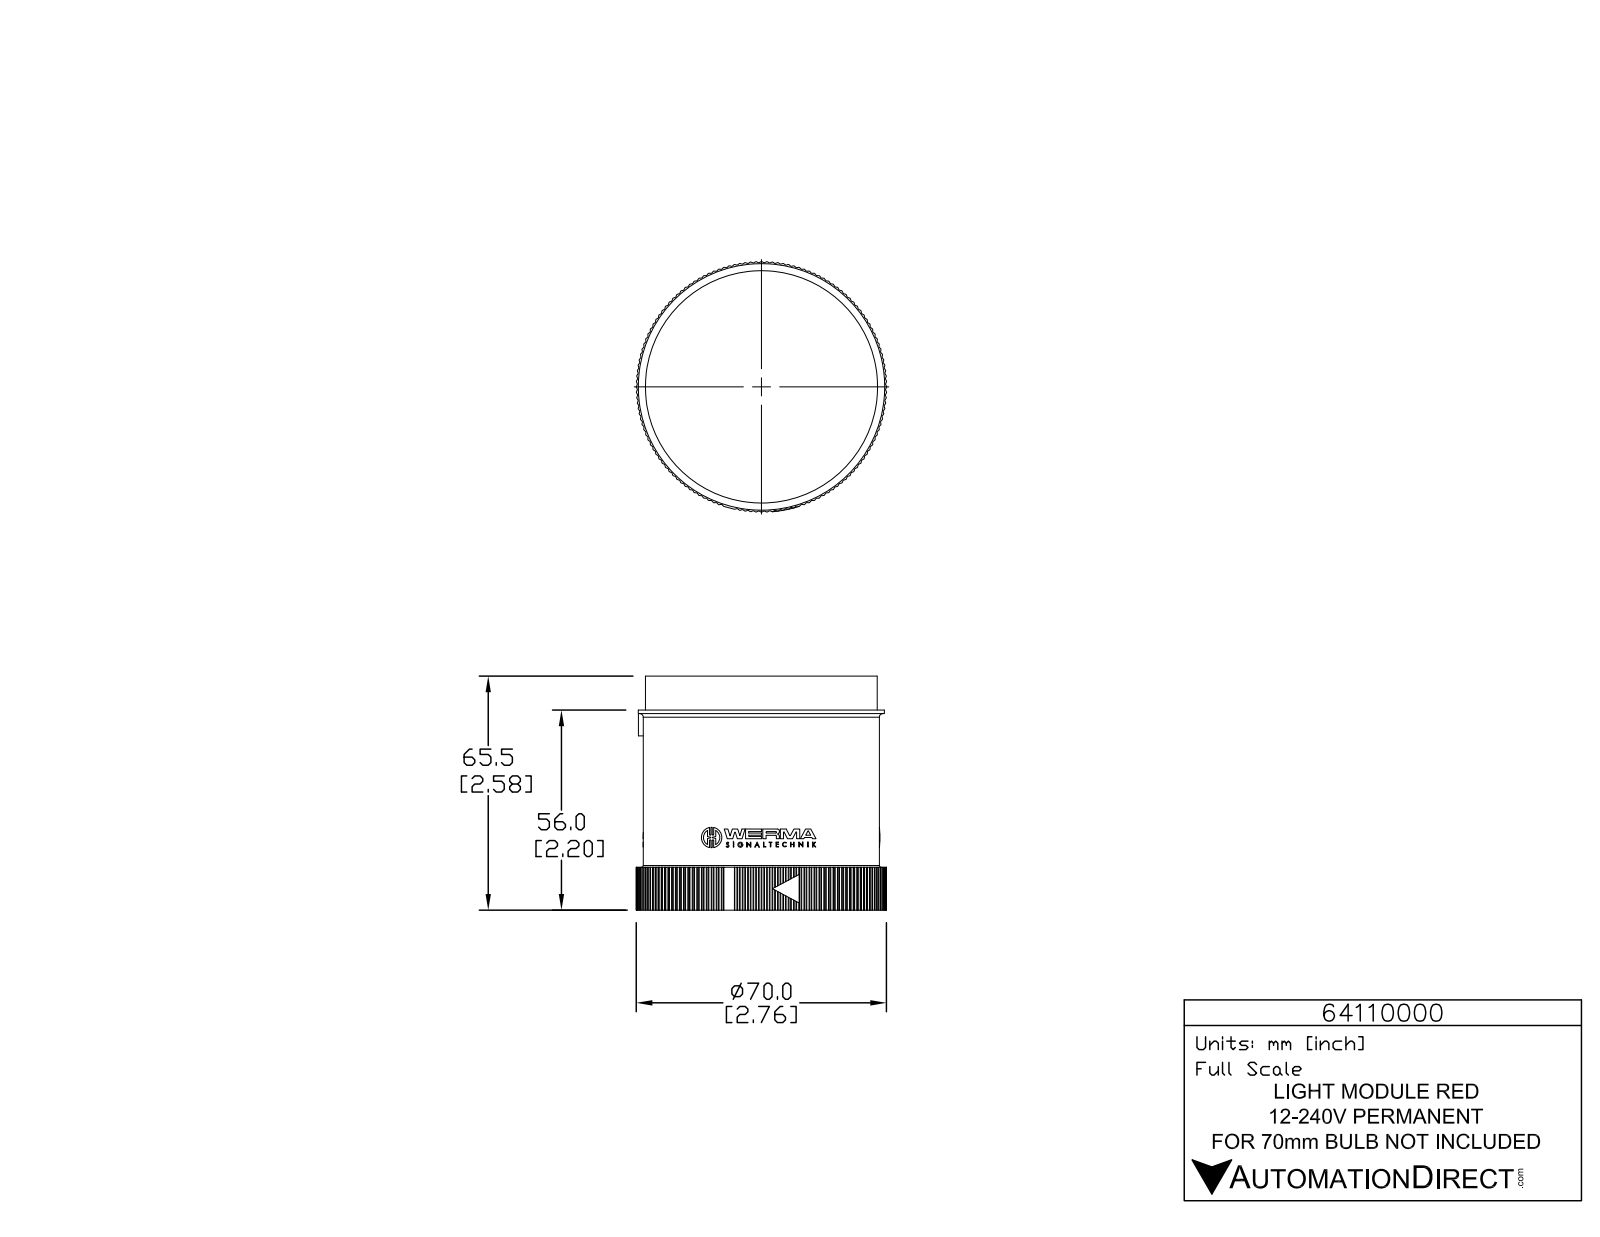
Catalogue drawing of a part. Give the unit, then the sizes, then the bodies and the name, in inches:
Units: inches
Overall size (bounding box): 2.762 × 2.762 × 2.579
Round holes (diameter × count): ⌀0.039 ×3, ⌀2.575 ×1
Round bosses / shafts (diameter × count): ⌀0.226 ×3, ⌀0.056 ×3, ⌀2.717 ×1, ⌀2.606 ×1, ⌀2.559 ×1
Partial cylindrical surfaces — rounded edges, fillets, slot ends (radius × count): R0.008 ×285, R0.008 ×6, R0.008 ×6, R0.008 ×6, R0.131 ×6, R0.004 ×3, R0.005 ×3, R0.008 ×3
Main face-to-face distances: 2.201, 2.451, 0.378, 2.579, 2.205, 1.827, 0.374, 2.452, 0.472, 0.094
Volume: 12.02 in³ · Surface area: 37.48 in²
Bodies: 1 solid, 1400 faces (832 planar, 563 cylindrical, 5 other)
Part name (STEP PRODUCT): 64110000
STEP written by: SolidWorks 2015 (AUTOMOTIVE_DESIGN)
